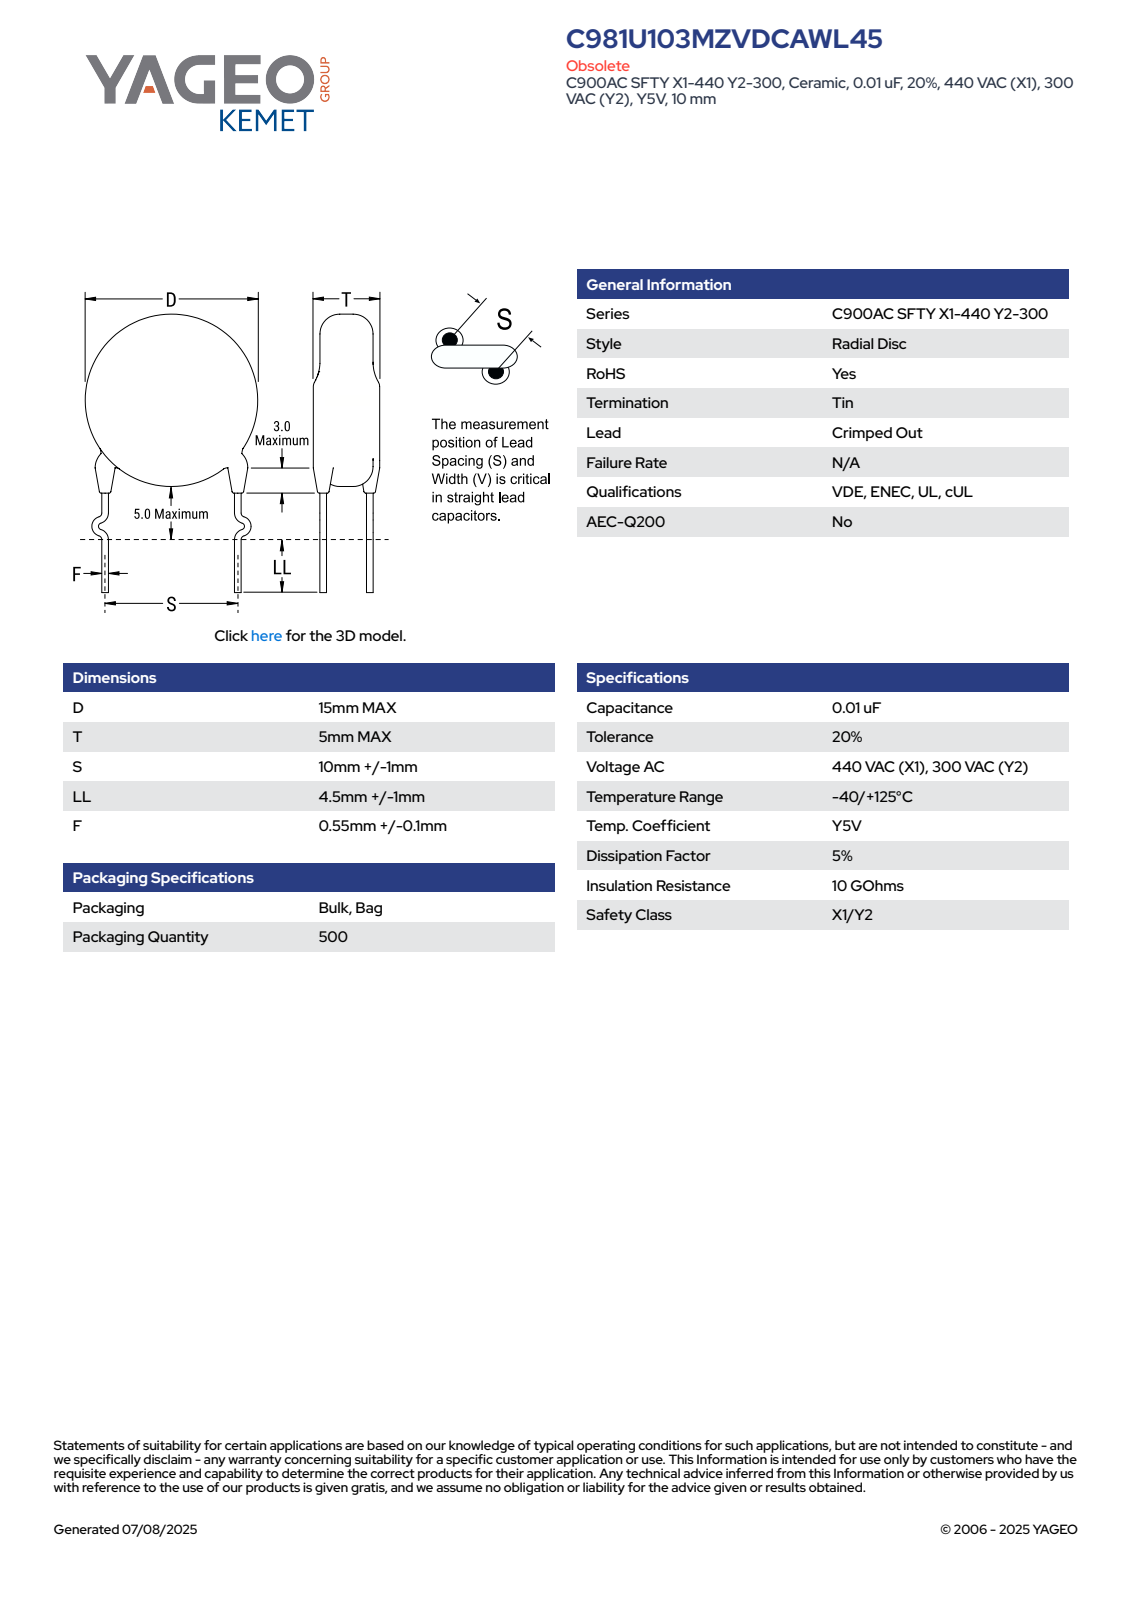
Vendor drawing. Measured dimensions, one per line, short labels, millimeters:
name: CCD_KCOC900_D15T5S10LL5.5F0.55
written by: SolidWorks 2014 (AUTOMOTIVE_DESIGN)
unit: mm
bodies: 4 solids, 85 faces (63 planar, 6 cylindrical, 16 other)
size: 25.5 × 15.21 × 5
volume: 877 mm³; area: 629 mm²
bosses: 2× ⌀1.2, 1× ⌀15
face distances: 5, 8.29, 6.74, 1.55, 0.42, 0.68, 6.37, 1.26, 0.97, 0.58
